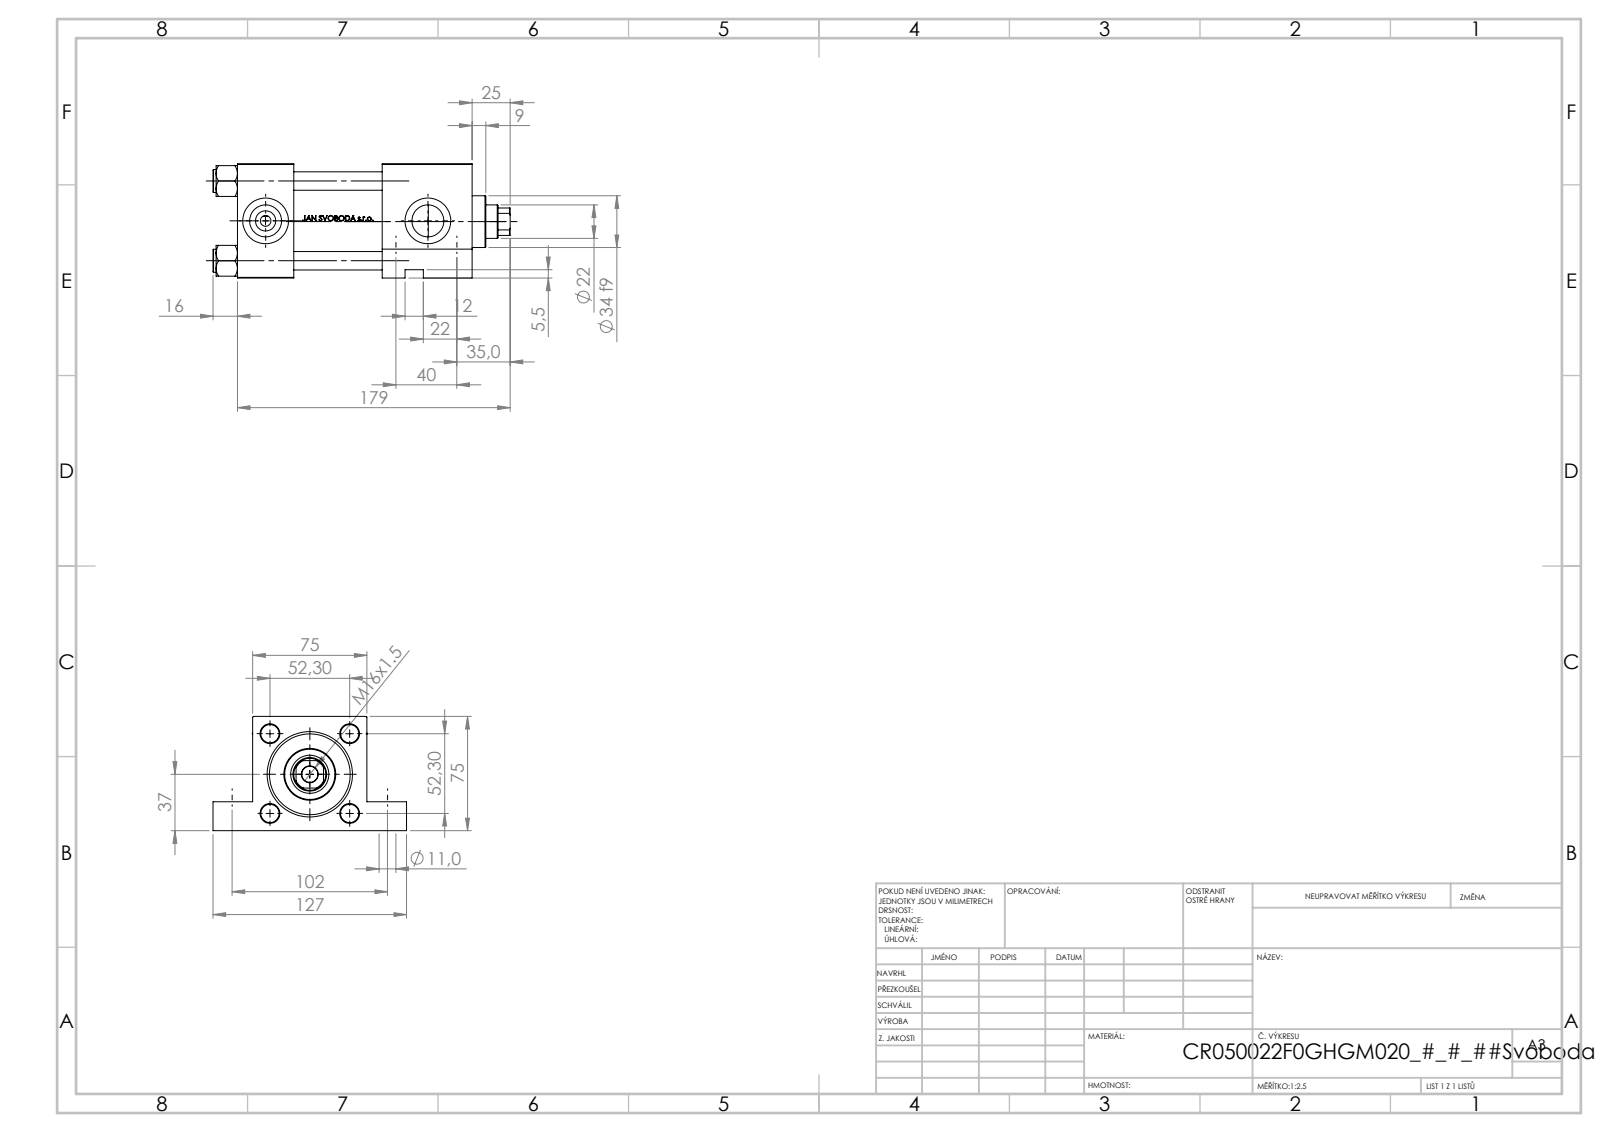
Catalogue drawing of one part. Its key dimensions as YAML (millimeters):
part_name: "V215_VC_A; NUT_M5_F; V215CR_VCP_F; V215CR_F_Body (+1 more)"
step_written_by: "SolidWorks 2019 (CONFIG_CONTROL_DESIGN)"
units: millimeters
bodies: {solids: 11, faces: 1103, planar: 437, cylindrical: 126, other: 540}
overall_size: [195, 127, 75]
volume: 706482
surface_area: 156148
round_holes:
  - {diameter: 12, count: 4}
  - {diameter: 7, count: 2}
  - {diameter: 11, count: 2}
  - {diameter: 11, count: 2}
  - {diameter: 20.96, count: 2}
  - {diameter: 30, count: 2}
  - {diameter: 10.5, count: 1}
  - {diameter: 22, count: 1}
  - {diameter: 25, count: 1}
  - {diameter: 41, count: 1}
  - {diameter: 50, count: 1}
  - {diameter: 53, count: 1}
round_bosses_or_shafts:
  - {diameter: 15, count: 4}
  - {diameter: 56, count: 1}
  - {diameter: 34, count: 1}
partial_cylinders:
  - {radius: 10.5, count: 1}
face_to_face_distances: [75, 37, 117, 154, 95, 58, 59, 19, 56, 125.3]
hole_center_spacings: [52.3, 36.63, 37.34, 40, 73.96, 102, 109.56, 106.5]
